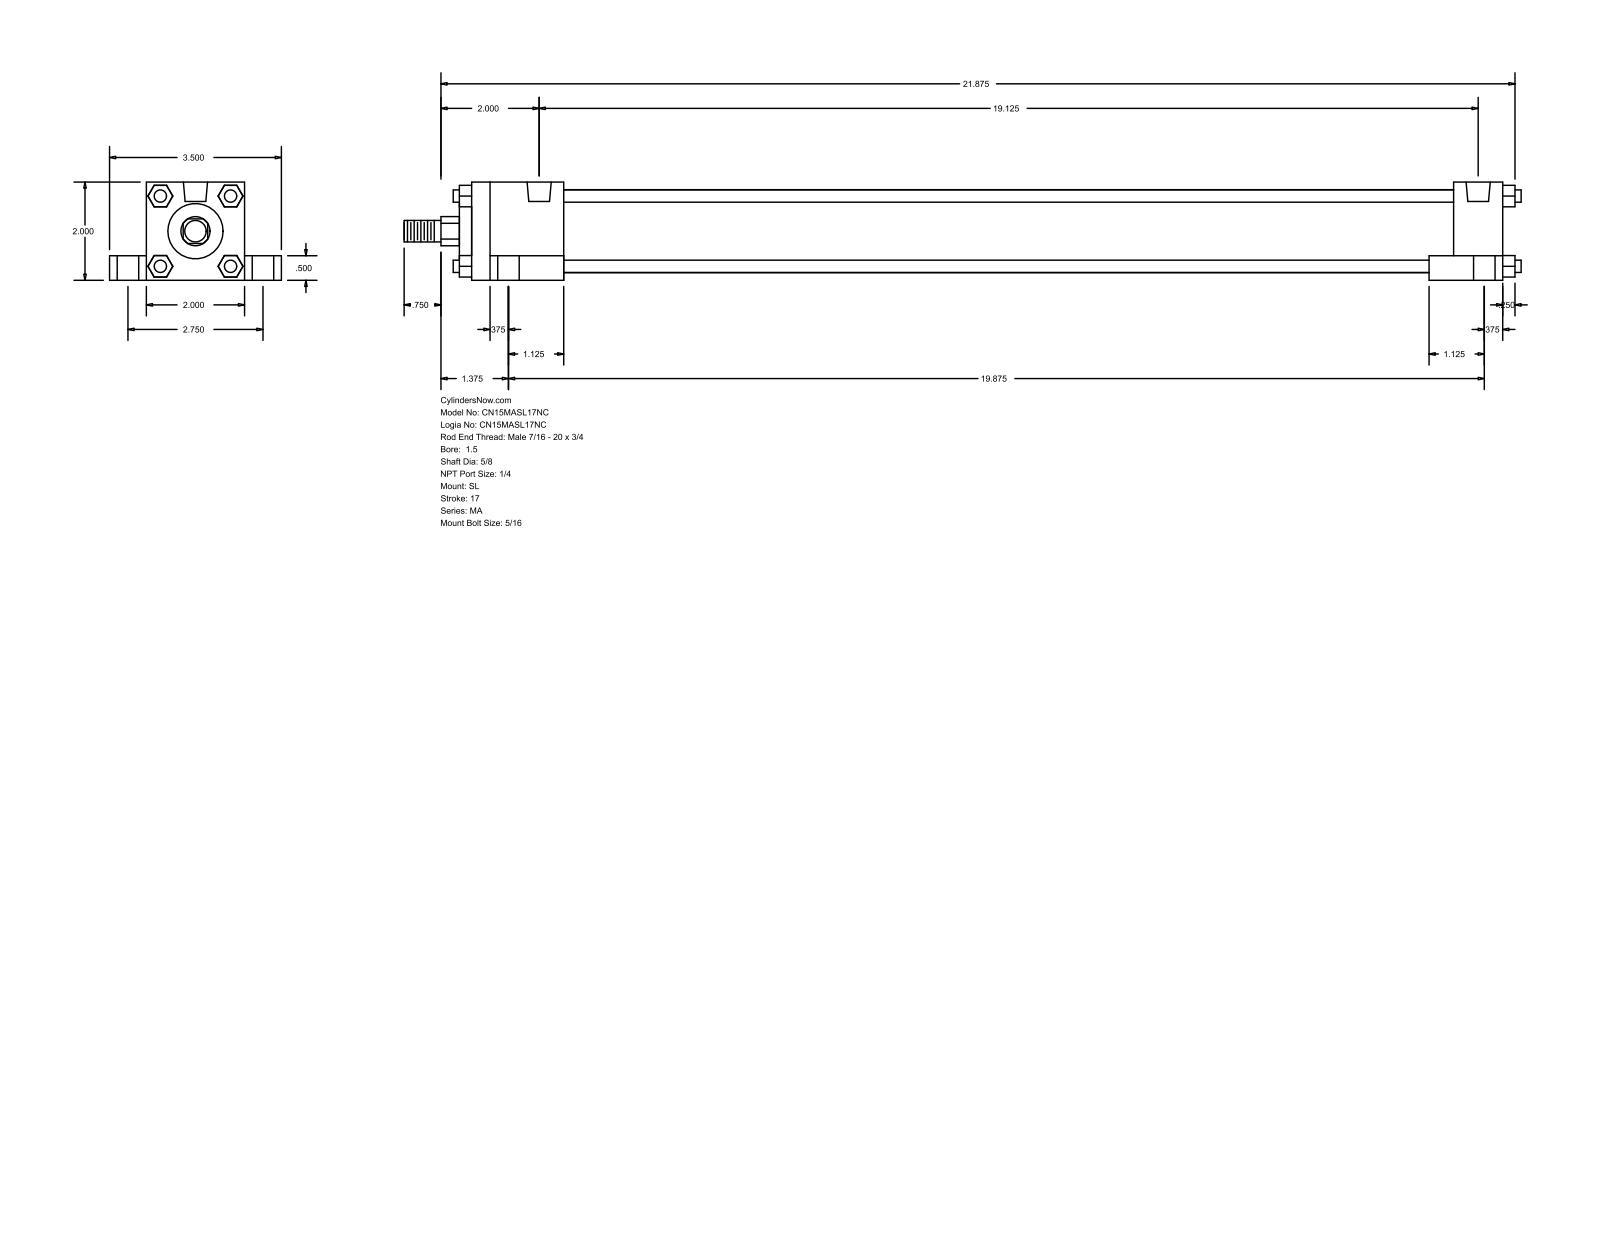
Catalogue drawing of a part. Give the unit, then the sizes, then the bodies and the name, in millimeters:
Units: millimetres
Overall size (bounding box): 577.85 × 88.9 × 50.8
Round holes (diameter × count): ⌀7.94 ×4, ⌀11.11 ×4, ⌀17.46 ×4, ⌀12.49 ×2
Round bosses / shafts (diameter × count): ⌀6.35 ×4, ⌀42.93 ×1, ⌀28.57 ×1, ⌀15.88 ×1, ⌀11.11 ×1
Partial cylindrical surfaces — rounded edges, fillets, slot ends (radius × count): R7.54 ×1
Main face-to-face distances: 50.8, 19.05, 38.1, 69.85, 12.7, 533.39, 6.35, 9.52, 539.74, 508
Hole centre spacings: 35.06, 38.36, 69.84, 485.78, 490.2, 502.87, 504.83, 509.64
Bodies: 0 solids, 148 faces (112 planar, 36 cylindrical, 0 other)
Part name (STEP PRODUCT): MA_SL__0150_0.625
STEP written by: GSSL Pune (CONFIG_CONTROL_DESIGN)
